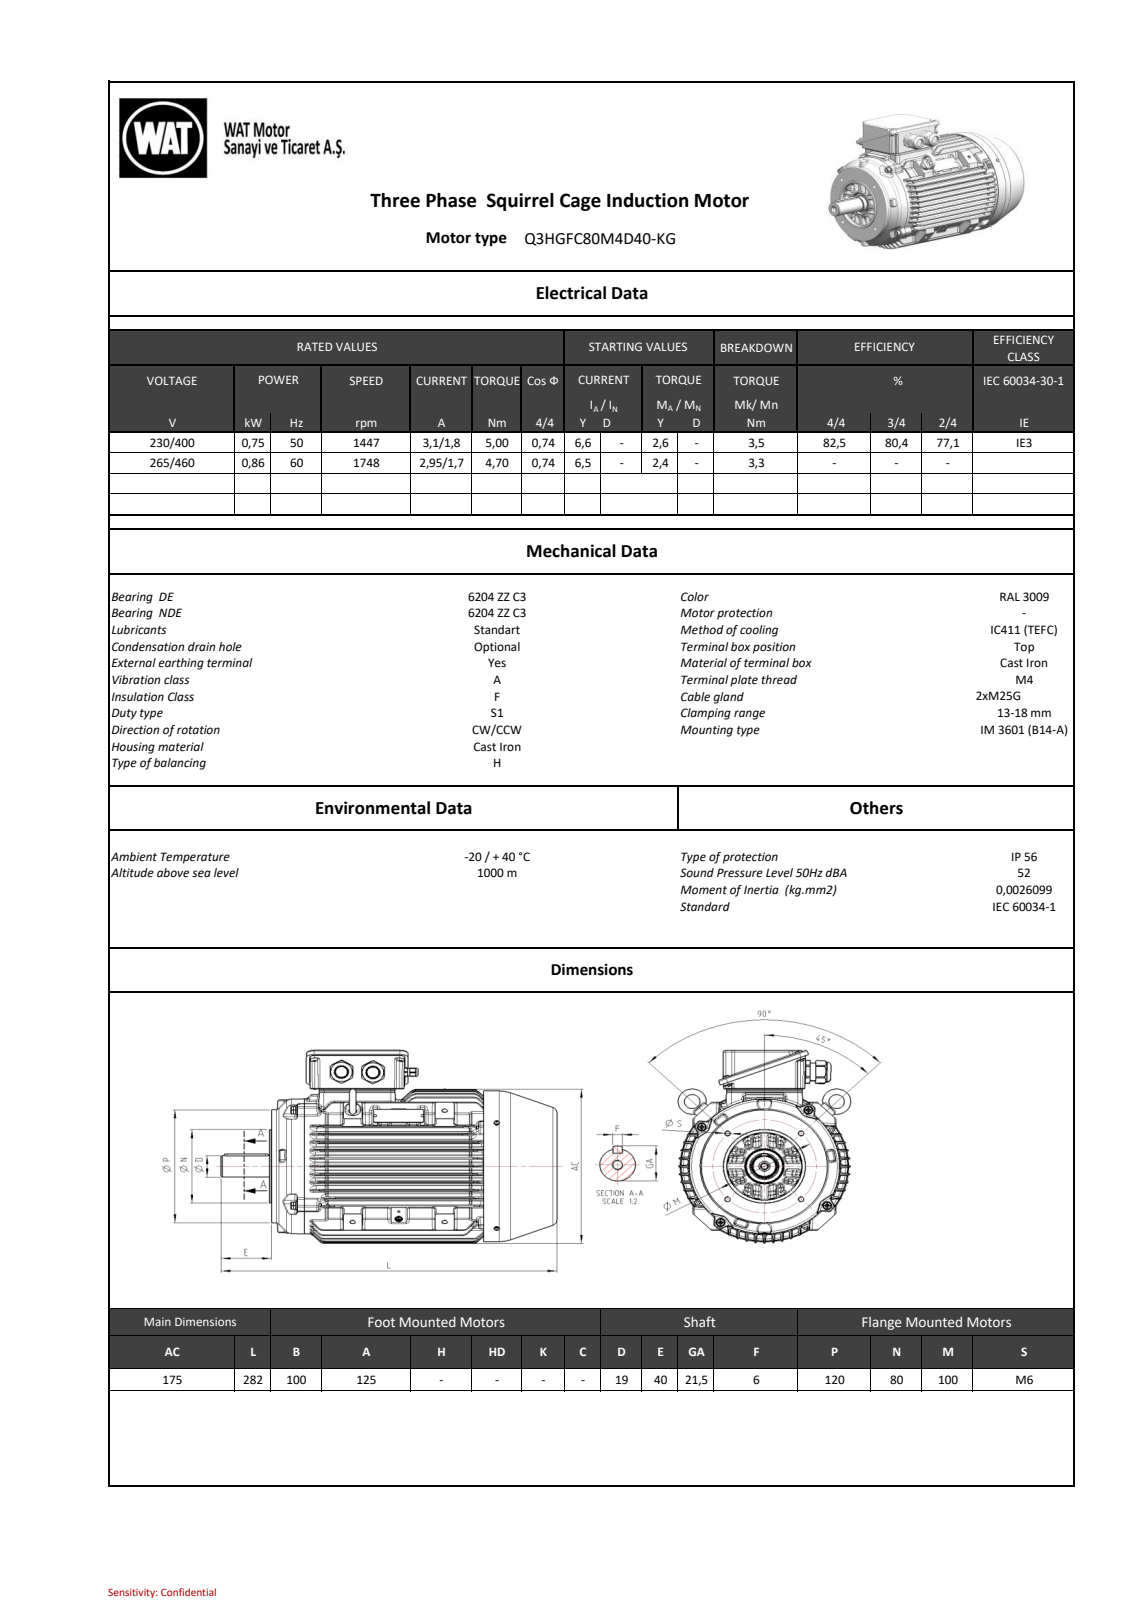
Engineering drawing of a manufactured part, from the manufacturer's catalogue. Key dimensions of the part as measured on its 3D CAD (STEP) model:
Part name (STEP PRODUCT): 260051B46F5629n7
STEP written by: SIEMENS PLM Software NX 11.0 (AUTOMOTIVE_DESIGN)
Units: millimetres
Bodies: 0 solids, 2823 faces (785 planar, 812 cylindrical, 1226 other)
Overall size (bounding box): 281.76 × 232.47 × 221.33
Round holes (diameter × count): ⌀5 ×5, ⌀10 ×3, ⌀2.5 ×2, ⌀17.2 ×2, ⌀6.4 ×1, ⌀6.5 ×1, ⌀27.8 ×1, ⌀28 ×1, ⌀168 ×1, ⌀170 ×1
Round bosses / shafts (diameter × count): ⌀20 ×4, ⌀9.2 ×3, ⌀8.65 ×3, ⌀8.5 ×3, ⌀8 ×3, ⌀5 ×3, ⌀27.7 ×2, ⌀25.25 ×2
Partial cylindrical surfaces — rounded edges, fillets, slot ends (radius × count): R1.5 ×323, R2.5 ×57, R1.8 ×38, R1 ×30, R0.2 ×23, R2 ×23, R4 ×20, R5 ×12
Main face-to-face distances: 41.78, 62.56, 241.76, 199.98, 3.01, 3, 1.5, 1.53, 2.98, 59.58
Hole centre spacings: 70.71, 50, 100, 40, 49.99, 50.01, 74.99, 77.95
